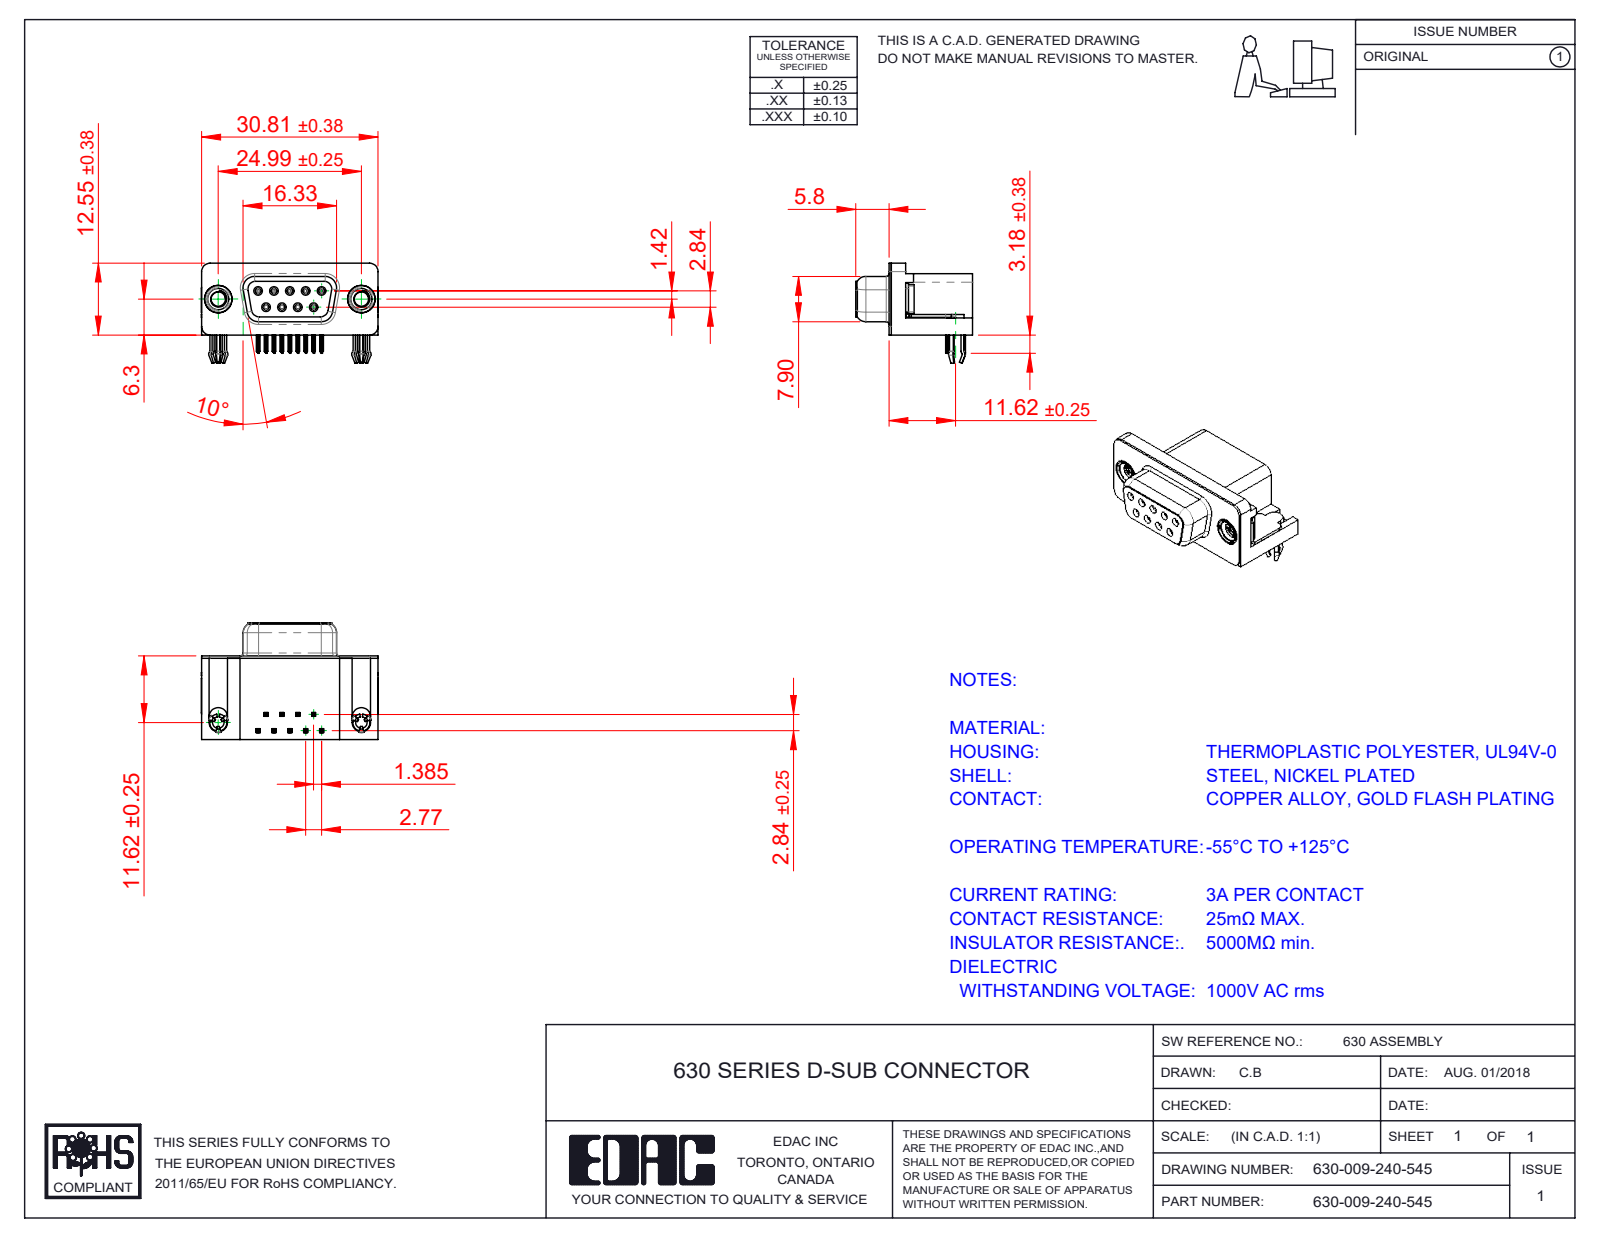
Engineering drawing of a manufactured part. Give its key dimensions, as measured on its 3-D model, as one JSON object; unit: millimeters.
{"part_name": "630 Housing_09 Socket; 630 3 Prong Board Lock; 630-009-240-545; 630 Contact Bottom (+3 more)", "step_written_by": "SolidWorks 2020 (CONFIG_CONTROL_DESIGN)", "units": "millimeters", "bodies": {"solids": 15, "faces": 1674, "planar": 720, "cylindrical": 426, "other": 528}, "overall_size": [30.89, 20.4, 17.48], "volume_mm3": 4208, "surface_area_mm2": 5511, "round_holes": [[0.8, 9], [0.9, 9], [2, 2], [2.5, 2], [4, 2], [4.8, 2], [5, 2]], "round_bosses_or_shafts": [[1.2, 9], [4.9, 2], [4.75, 2], [3.9, 2], [3, 2]], "partial_cylinders_radius": [[0.1, 72], [0.15, 36], [0.35, 18], [1, 18], [0.25, 12], [0.34, 9], [1.35, 8], [1.6, 8]], "face_to_face_distances": [0.4, 14.6, 14.2, 10.34, 6.2, 2.9, 2.5, 11.7, 0.35, 0.5], "hole_center_spacings": [3.16, 2.77, 5.54, 5.03, 5.04, 8.31, 7.48, 7.49]}
